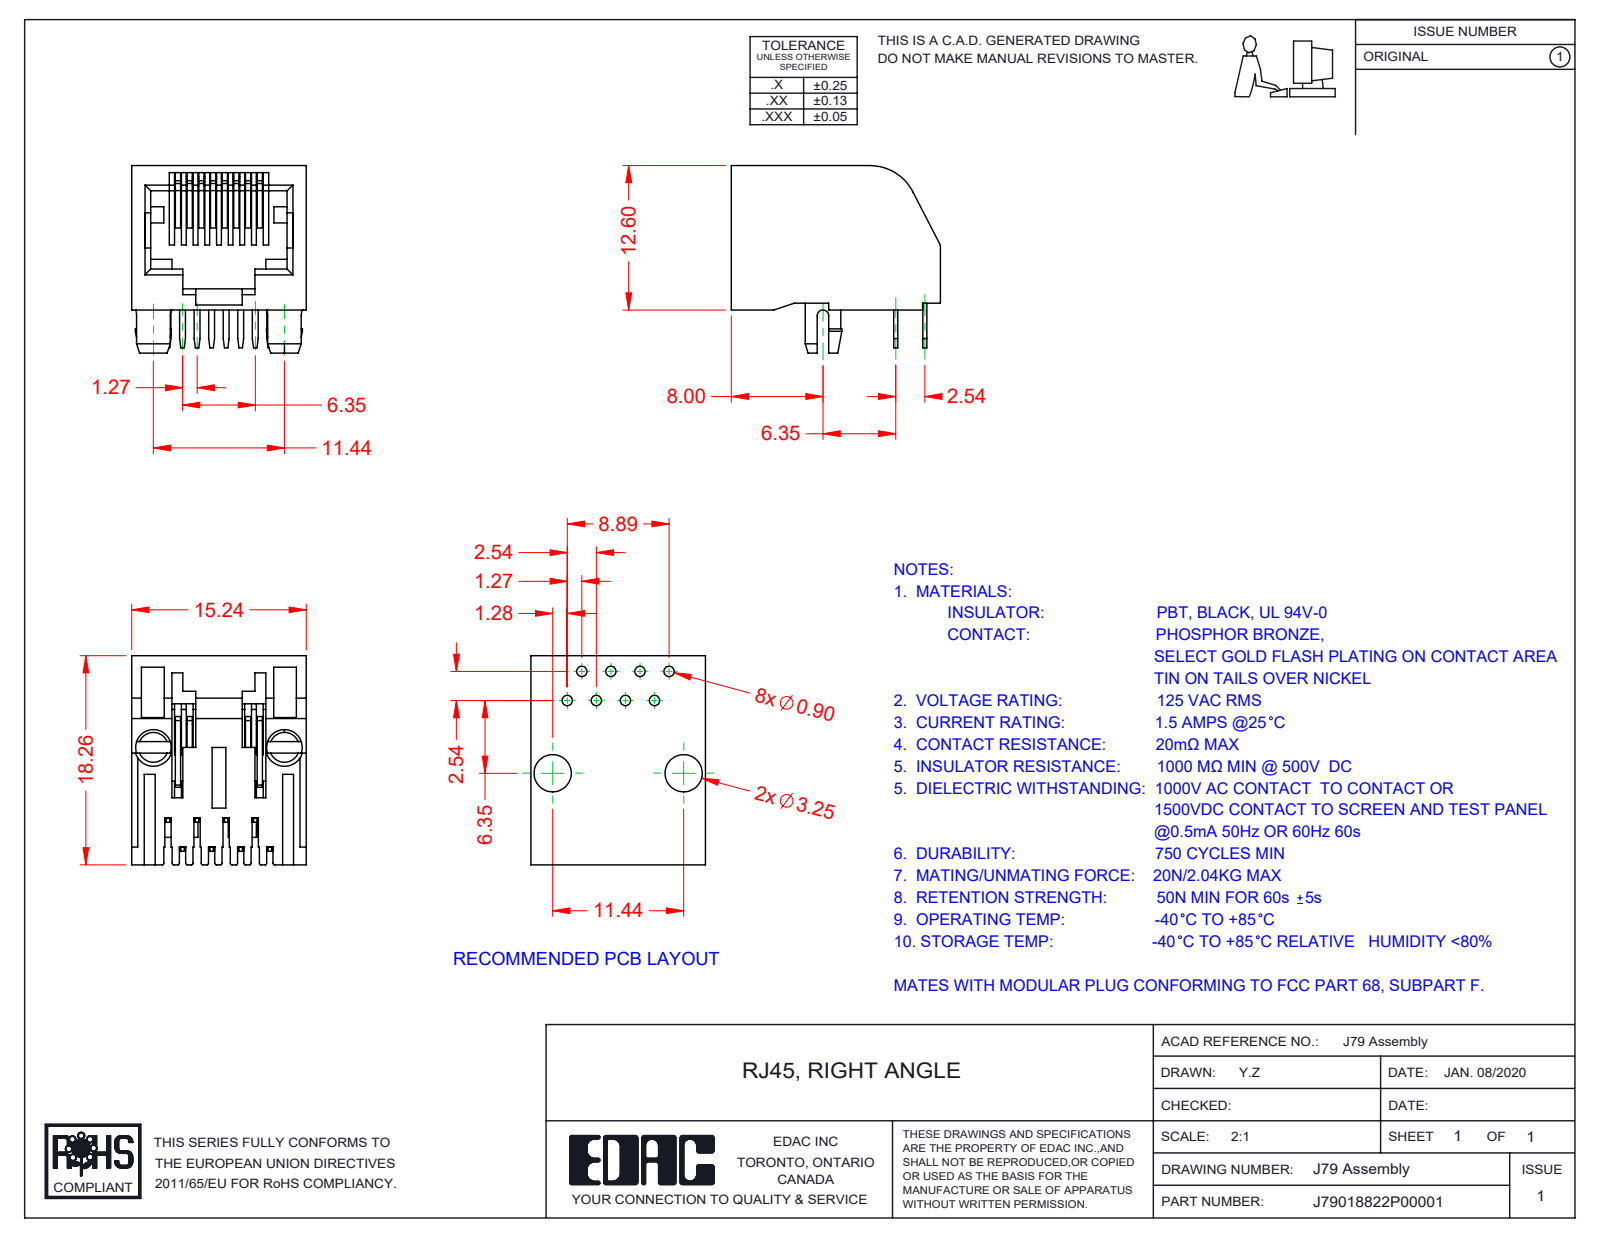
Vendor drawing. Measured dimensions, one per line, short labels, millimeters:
name: 79 Insulator; RJ79018822P00001; 79 Contacts
written by: SolidWorks 2016 (CONFIG_CONTROL_DESIGN)
unit: mm
bodies: 9 solids, 574 faces (424 planar, 144 cylindrical, 6 other)
size: 18.26 × 16.36 × 15.24
volume: 1 496 mm³; area: 3 263 mm²
bosses: 2× ⌀3.1
rounds: 16× R0.15, 7× R0.5, 3× R0.72, 2× R0.36, 2× R1.65, 2× R1.8, 2× R2.16, 1× R0.2
face distances: 15.24, 2.04, 0.6, 12, 0.36, 4.08, 1.25, 9.8, 2.2, 8.2
